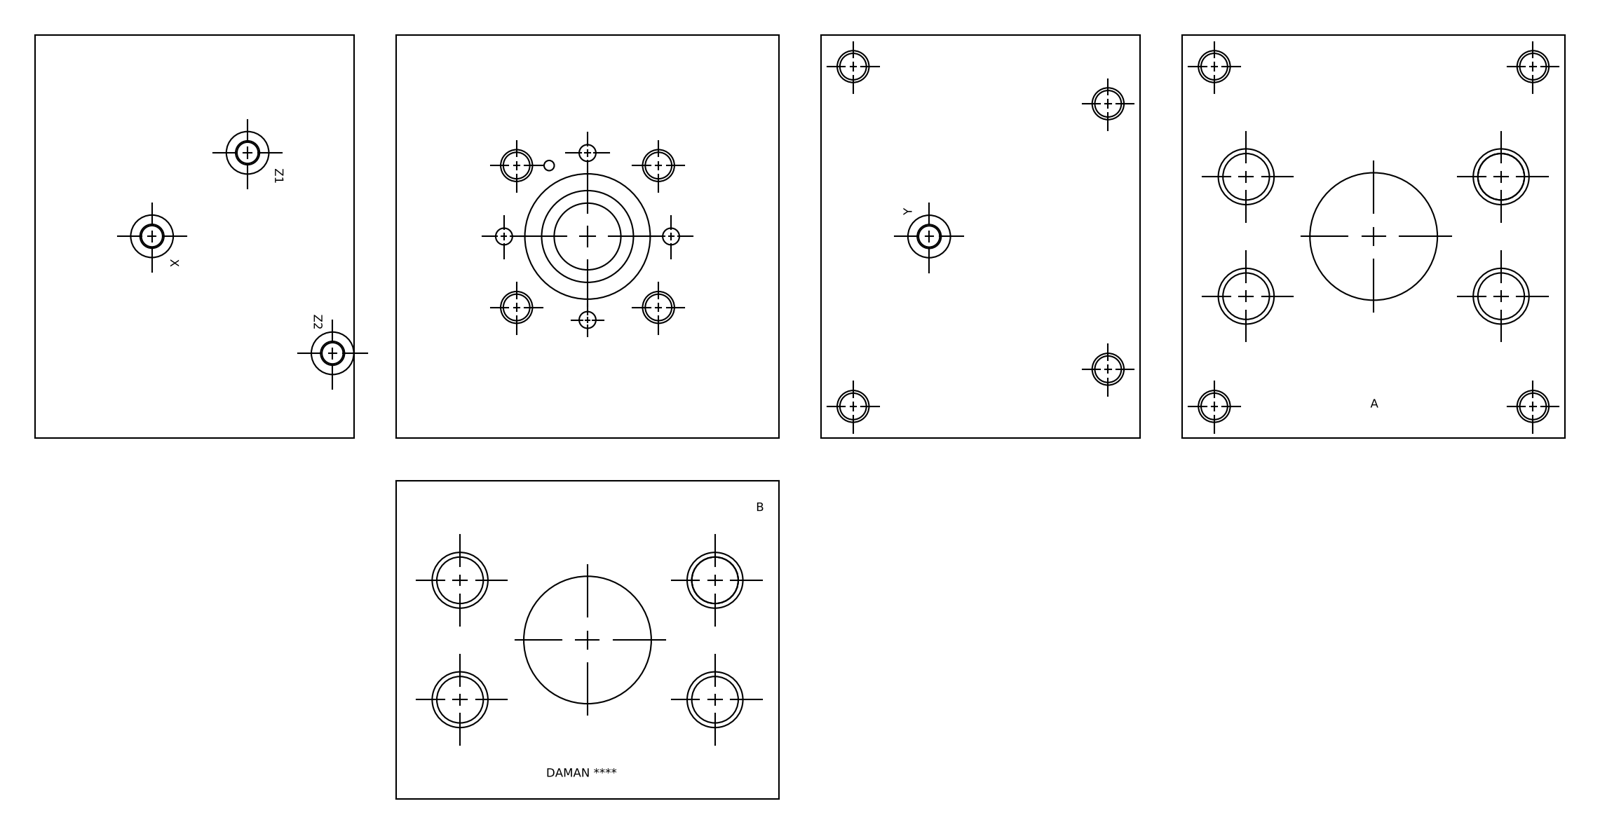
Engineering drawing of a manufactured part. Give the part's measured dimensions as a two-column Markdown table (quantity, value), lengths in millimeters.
| quantity | value |
| --- | --- |
| part name | Part_D40XA48F62_3D |
| STEP written by | Autodesk Inventor 2020 (CONFIG_CONTROL_DESIGN) |
| units | millimeters |
| bodies | 1 solid, 575 faces (364 planar, 70 cylindrical, 141 other) |
| overall size | 241.3 × 228.6 × 190.5 |
| volume | 9 272 000 mm³ |
| surface area | 411 290 mm² |
| round holes (diameter × count) | 16.66 × 12, 19.05 × 12, 24.99 × 8, 28.57 × 8, 10.01 × 4, 12.29 × 4, 14.27 × 4, 14.53 × 4, 25.02 × 4, 12.9 × 3, 76.2 × 2, 5.99 × 1 |
| main face-to-face distances | 190.5, 228.6, 241.3, 103.5, 87, 0.79, 227.81, 85.52, 17.98, 104.98 |
| hole center spacings | 84.15, 43.17, 101.83, 44.28, 50.01, 68.59, 70.72, 71.42 |
